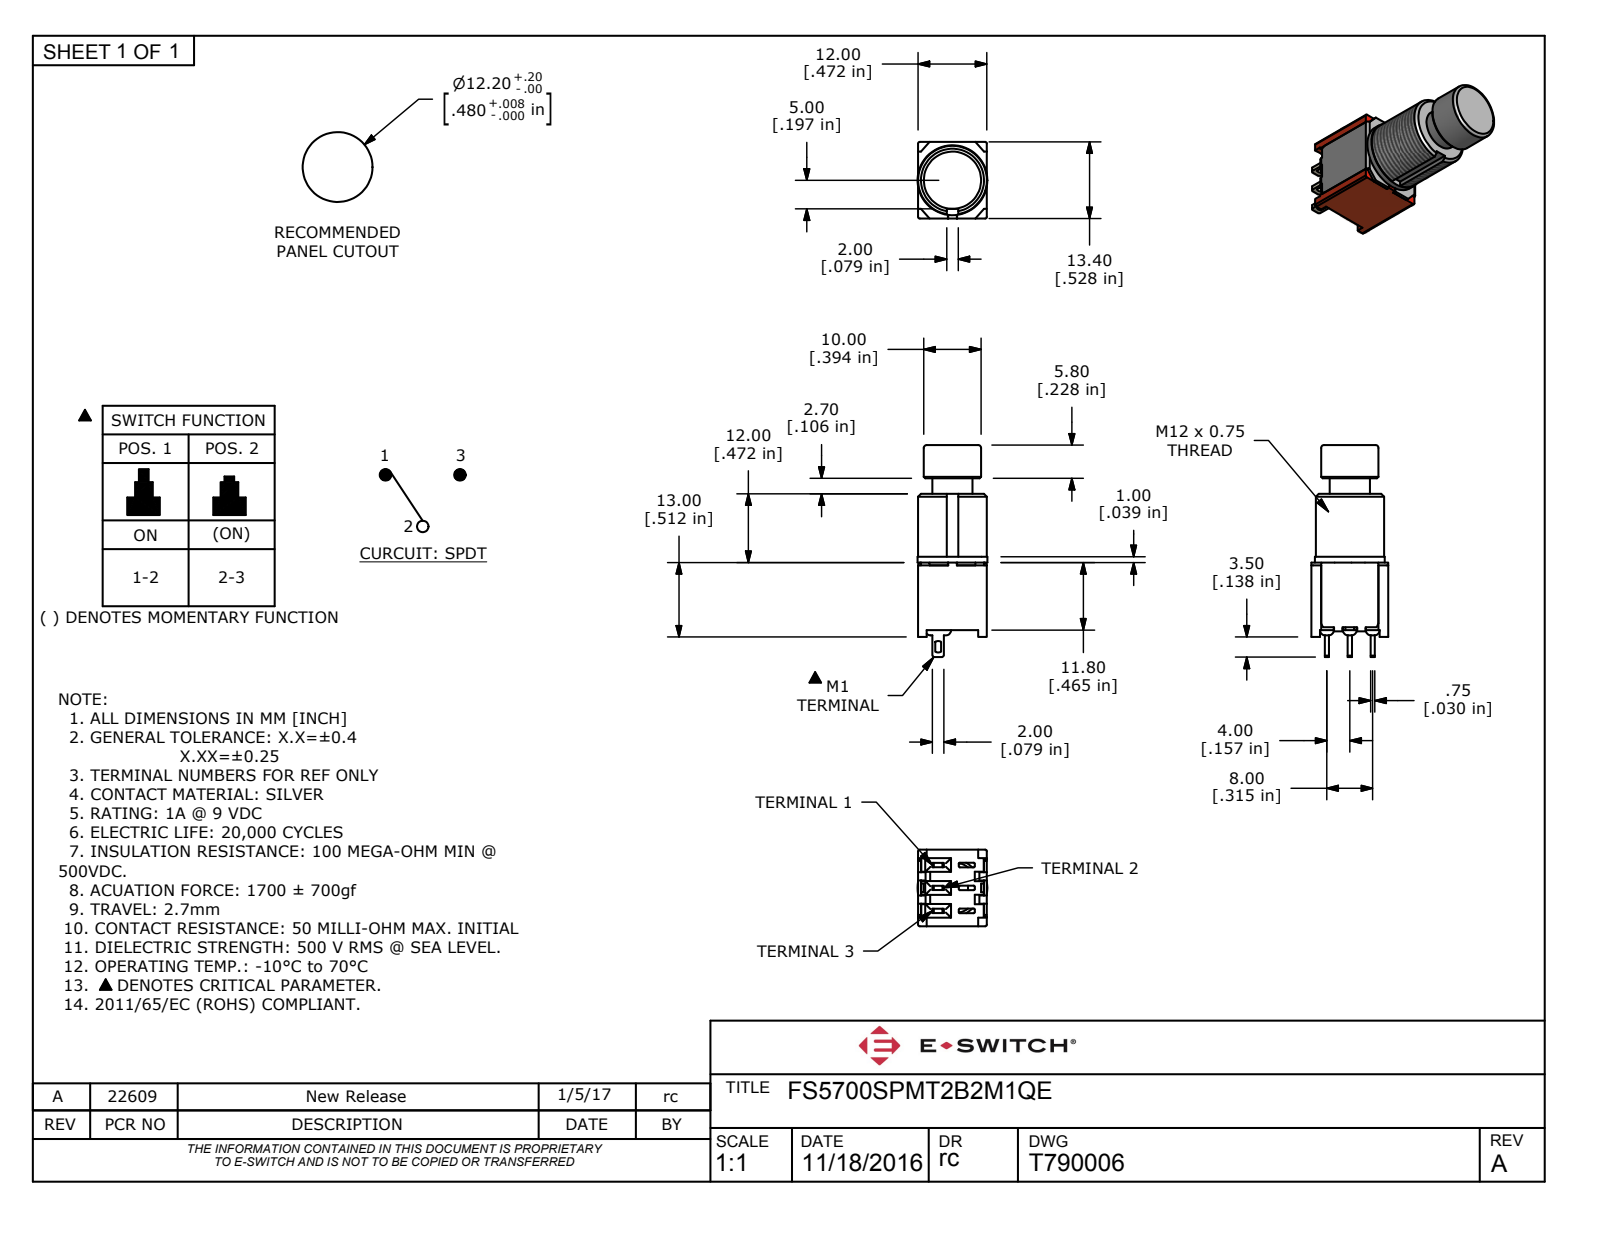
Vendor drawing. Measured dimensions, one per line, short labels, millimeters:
name: FS5700SPMT2B2M1QE
written by: Autodesk Inventor 2022 (AUTOMOTIVE_DESIGN)
unit: mm
bodies: 1 solid, 280 faces (212 planar, 65 cylindrical, 3 other)
size: 37 × 13.4 × 12.2
volume: 2 103 mm³; area: 3 280 mm²
holes: 1× ⌀9
bosses: 1× ⌀12.2, 1× ⌀12, 1× ⌀10, 1× ⌀7
rounds: 26× R0.2, 8× R0.9, 4× R0.3, 4× R0.5, 2× R0.1, 1× R1
face distances: 1.2, 0.5, 11, 10.8, 10.3, 0.7, 11.5, 0.55, 11.45, 0.65
